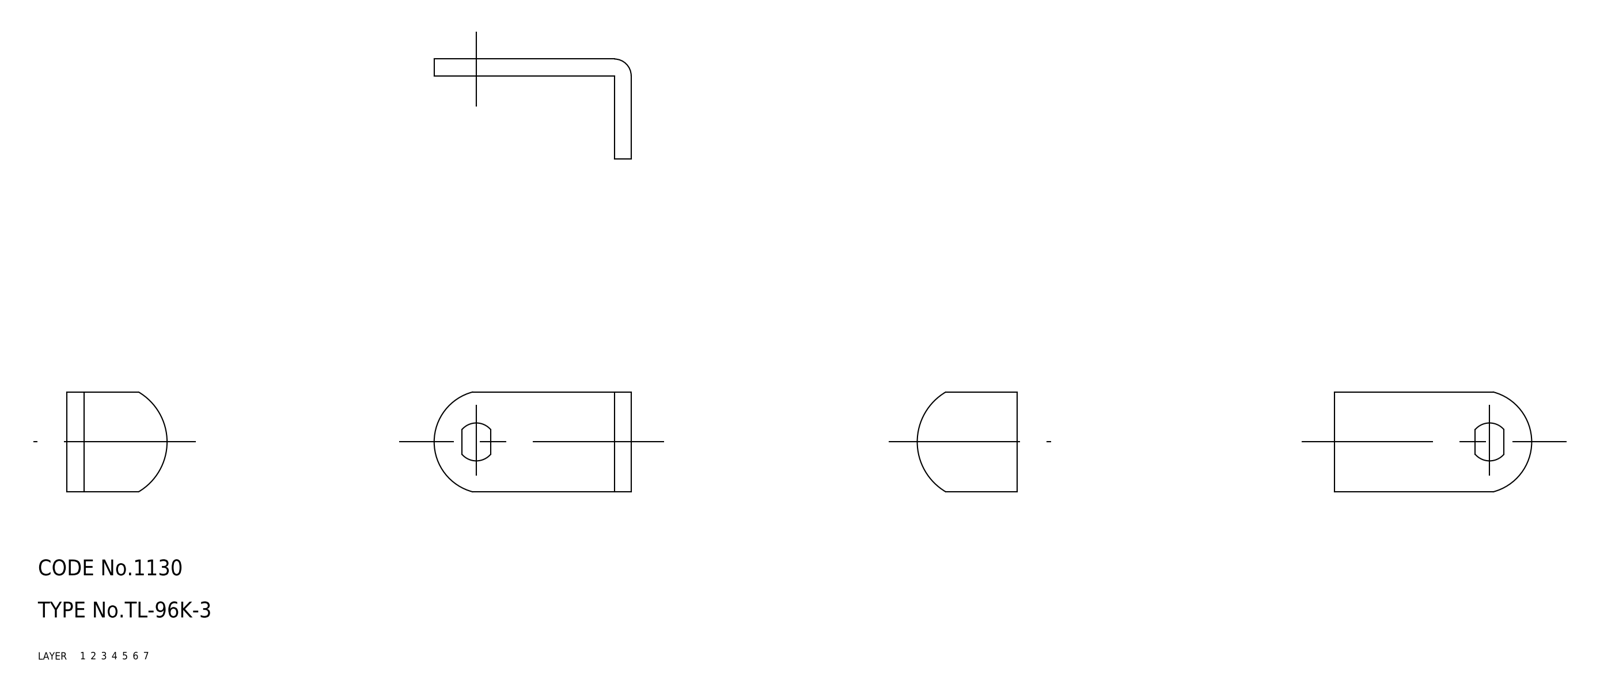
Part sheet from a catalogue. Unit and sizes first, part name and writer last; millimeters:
Units: millimetres
Overall size (bounding box): 37.4 × 19 × 19
Volume: 2 867 mm³ · Surface area: 2 272 mm²
Bodies: 1 solid, 13 faces (0 planar, 0 cylindrical, 13 other)
Part name (STEP PRODUCT): cam
STEP written by: CADfix (AUTOMOTIVE_DESIGN)
